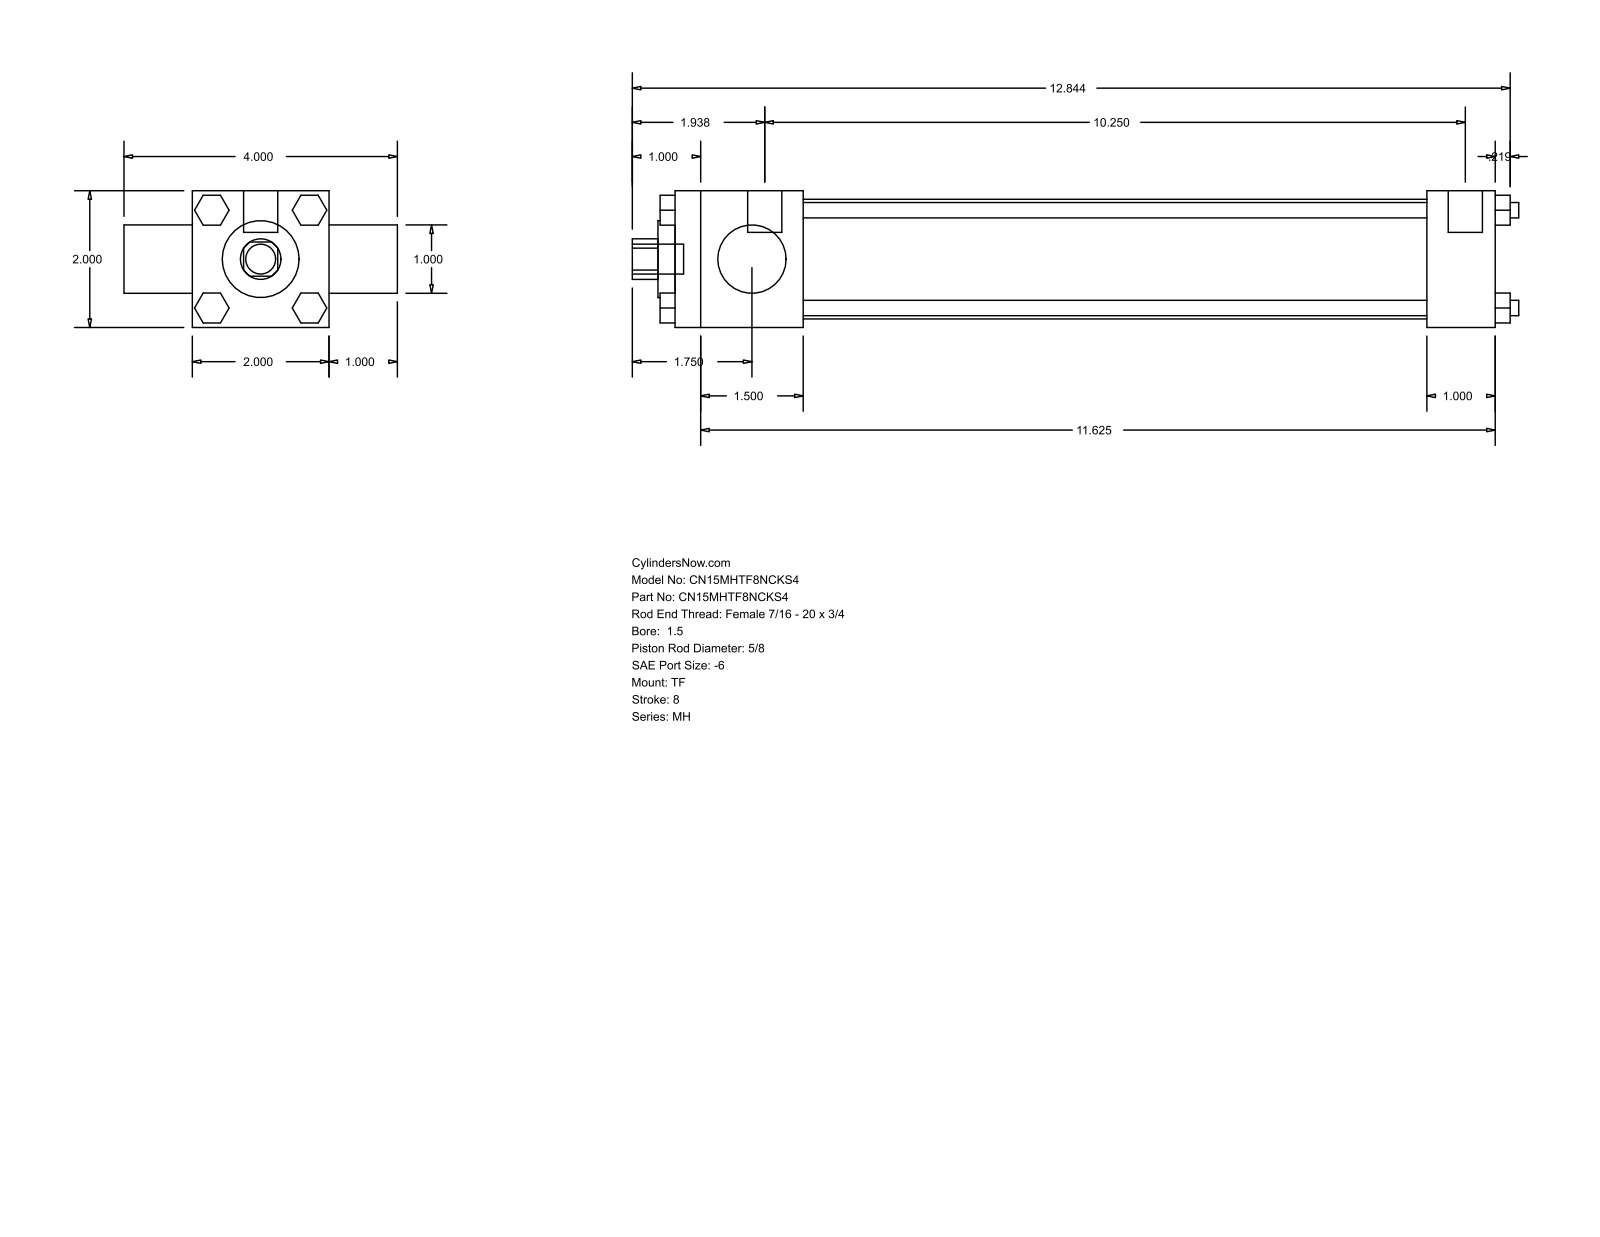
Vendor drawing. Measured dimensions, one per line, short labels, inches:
name: MH_TF__0150_0.625
written by: GSSL Pune (CONFIG_CONTROL_DESIGN)
unit: in
bodies: 0 solids, 120 faces (92 planar, 28 cylindrical, 0 other)
size: 12.969 × 4 × 2
holes: 1× ⌀0.625, 1× ⌀1, 1× ⌀1.125, 1× ⌀1.75
bosses: 4× ⌀0.225, 3× ⌀0.219, 2× ⌀0.5, 1× ⌀0.437
rounds: 1× R0.297
face distances: 2, 12, 1, 3, 1.875, 10.125, 11, 9.125, 1, 0.437
